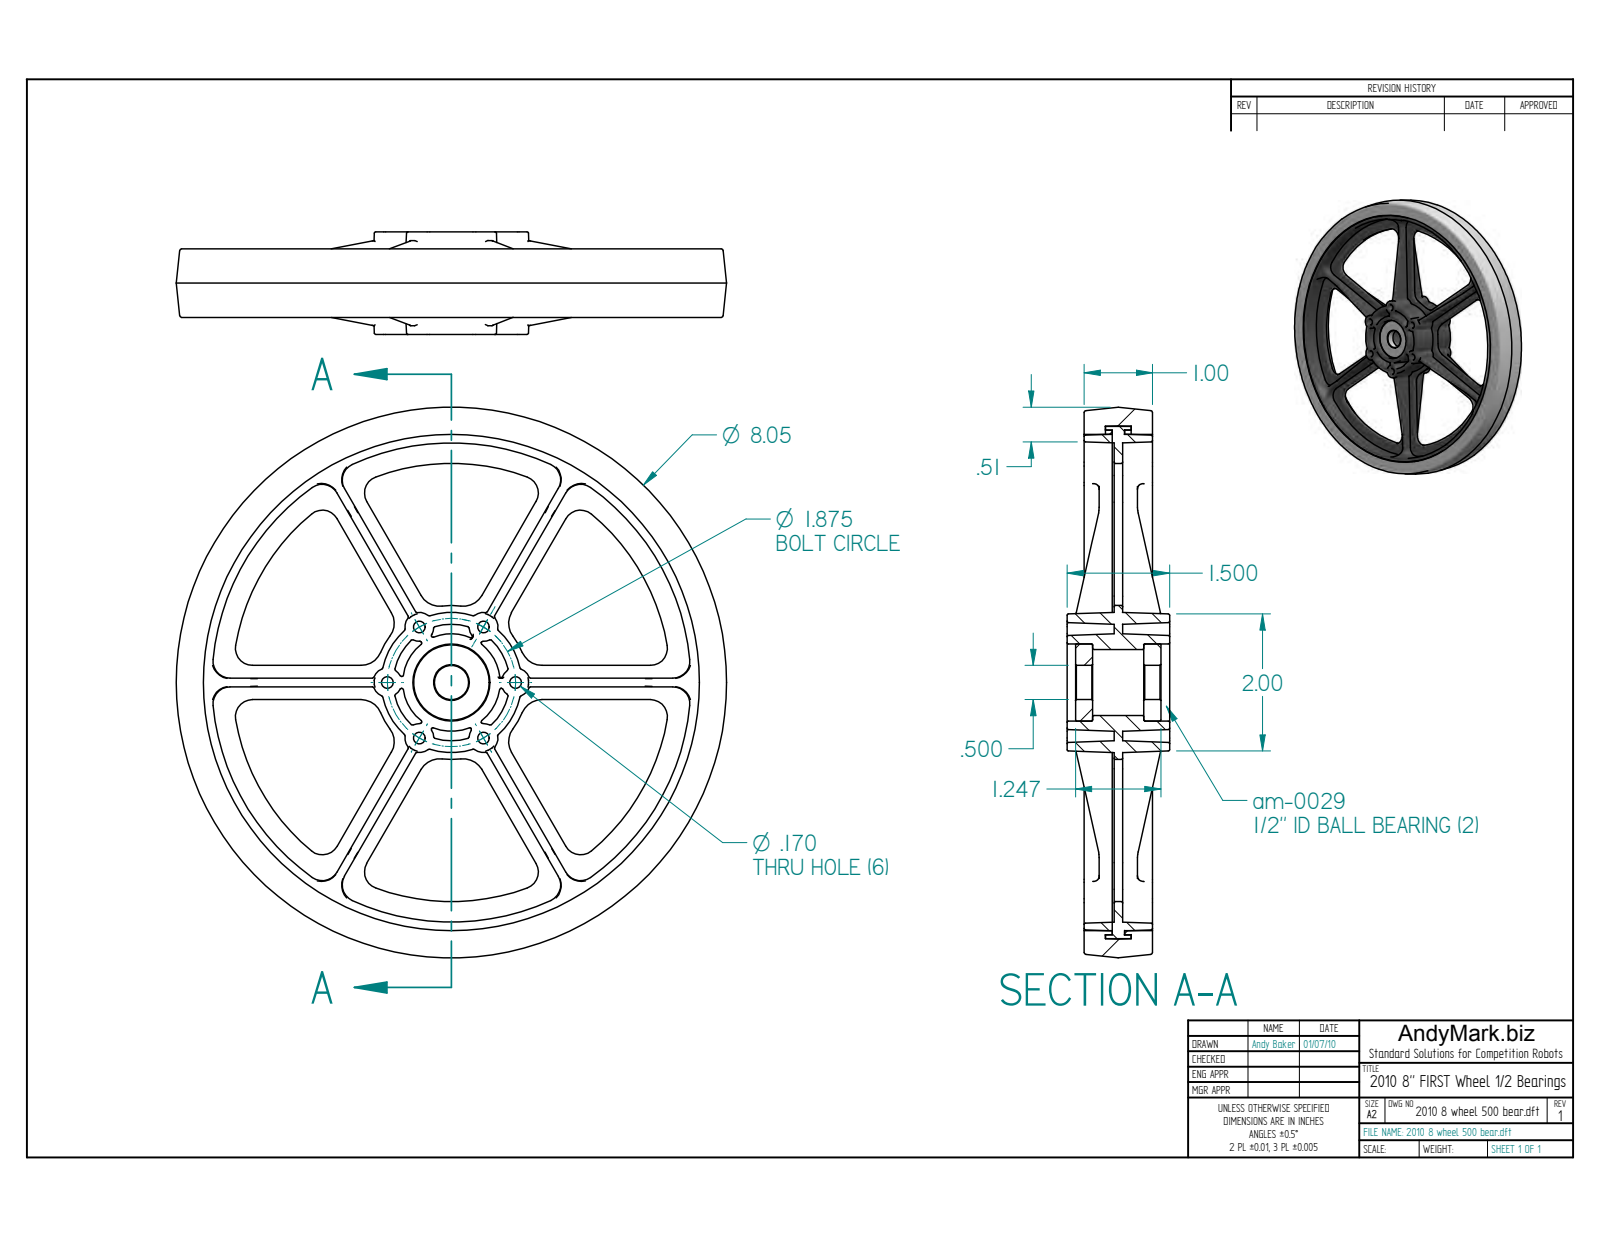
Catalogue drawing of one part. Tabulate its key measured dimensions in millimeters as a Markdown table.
| quantity | value |
| --- | --- |
| part name | 2010 8 tread; 2010 8 hub; r8 bearing |
| STEP written by | Unknown (CONFIG_CONTROL_DESIGN) |
| units | millimeters |
| bodies | 7 solids, 1946 faces (230 planar, 254 cylindrical, 1462 other) |
| overall size | 204.35 × 204.35 × 44.45 |
| volume | 574 932 mm³ |
| surface area | 292 951 mm² |
| round holes (diameter × count) | 4.32 × 6, 12.7 × 1, 24.43 × 1, 28.56 × 1, 184.15 × 1, 187.35 × 1, 190.09 × 1 |
| round bosses / shafts (diameter × count) | 187.3 × 1, 28.57 × 1 |
| partial cylindrical surfaces (radius × count) | 0.51 × 39, 6.35 × 12, 7.94 × 12, 28.57 × 1, 81.28 × 1 |
| main face-to-face distances | 12.7, 3.14, 11.13, 14.27, 25.4, 1.57, 10.41, 14.99, 2.29, 7.94 |
| hole center spacings | 23.81, 41.24, 47.62, 23.82 |
